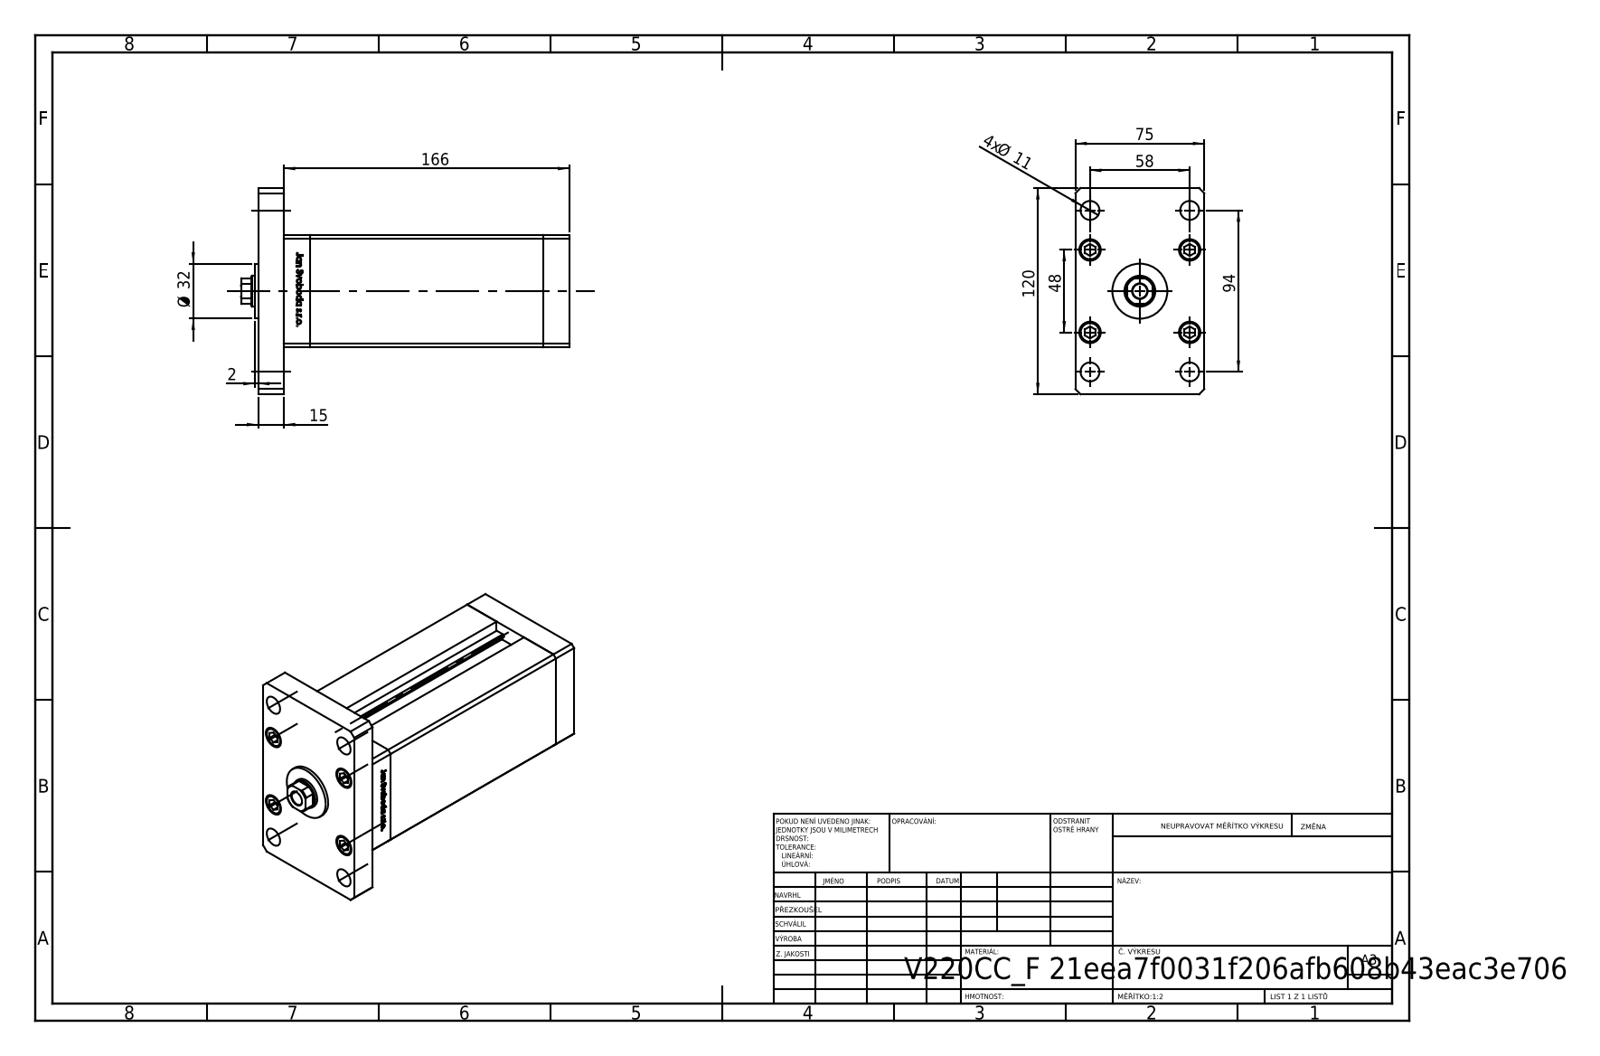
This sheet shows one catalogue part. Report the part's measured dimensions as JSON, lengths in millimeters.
{"part_name": "V220C BACK_F; V220C_F; V220C_FRONT_F; V220C_VC_F (+2 more)", "step_written_by": "SolidWorks 2019 (CONFIG_CONTROL_DESIGN)", "units": "millimeters", "bodies": {"solids": 19, "faces": 1308, "planar": 515, "cylindrical": 187, "other": 606}, "overall_size": [191, 120, 75], "volume_mm3": 848547, "surface_area_mm2": 159956, "round_holes": [[9, 5], [13.5, 5], [8, 4], [11, 4], [12.5, 4], [2, 2], [13.16, 2], [8.5, 1], [18, 1], [19.5, 1]], "round_bosses_or_shafts": [[12.5, 5], [8, 5], [32, 1]], "partial_cylinders_radius": [[0.93, 2], [8.5, 1]], "face_to_face_distances": [15, 75, 151, 166, 65, 30, 136, 181, 13, 153], "hole_center_spacings": [24, 23, 37.64, 55.23, 58, 62.39, 71, 91.68]}
